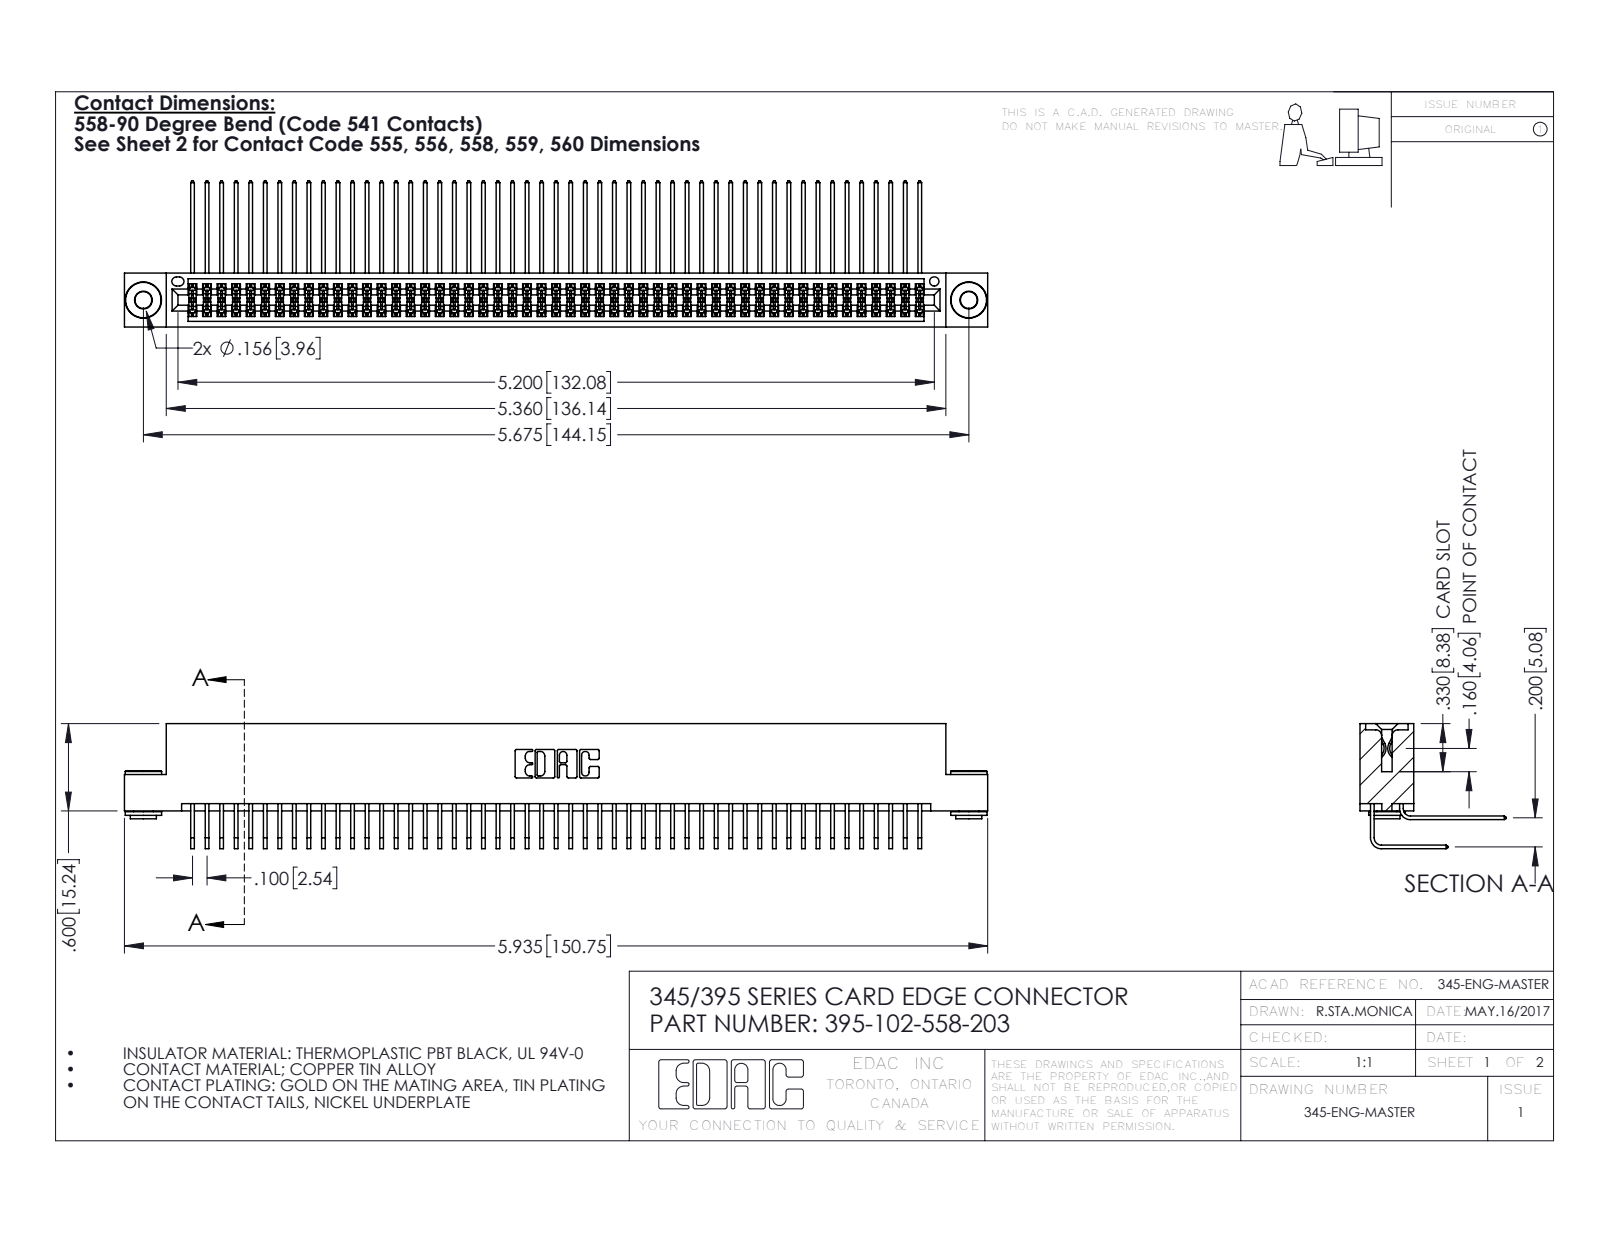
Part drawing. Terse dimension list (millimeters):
name: 395-102-558-203; 345-250-002_345-250-002-102; 345-292-001_558 Tail - 2; 345-292-001_558 559 Tail - 1 (+1 more)
written by: SolidWorks 2016 (CONFIG_CONTROL_DESIGN)
unit: mm
bodies: 105 solids, 5468 faces (3660 planar, 1800 cylindrical, 8 other)
size: 150.7 × 25.5 × 21.8
volume: 15 300 mm³; area: 25 810 mm²
holes: 2× ⌀2.9, 2× ⌀4, 1× ⌀1.6
bosses: 2× ⌀6.4, 2× ⌀4.6, 2× ⌀3.5
rounds: 154× R0.2, 22× R0.3, 6× R0.2, 6× R0.8, 3× R0.7, 2× R0.4, 2× R0.5, 2× R0.6
face distances: 1.8, 7.6, 5.1, 9.4, 0.6, 2.5, 6.9, 5.7, 0.6, 4.4
hole spacings: 6.9, 138.2, 144.1
